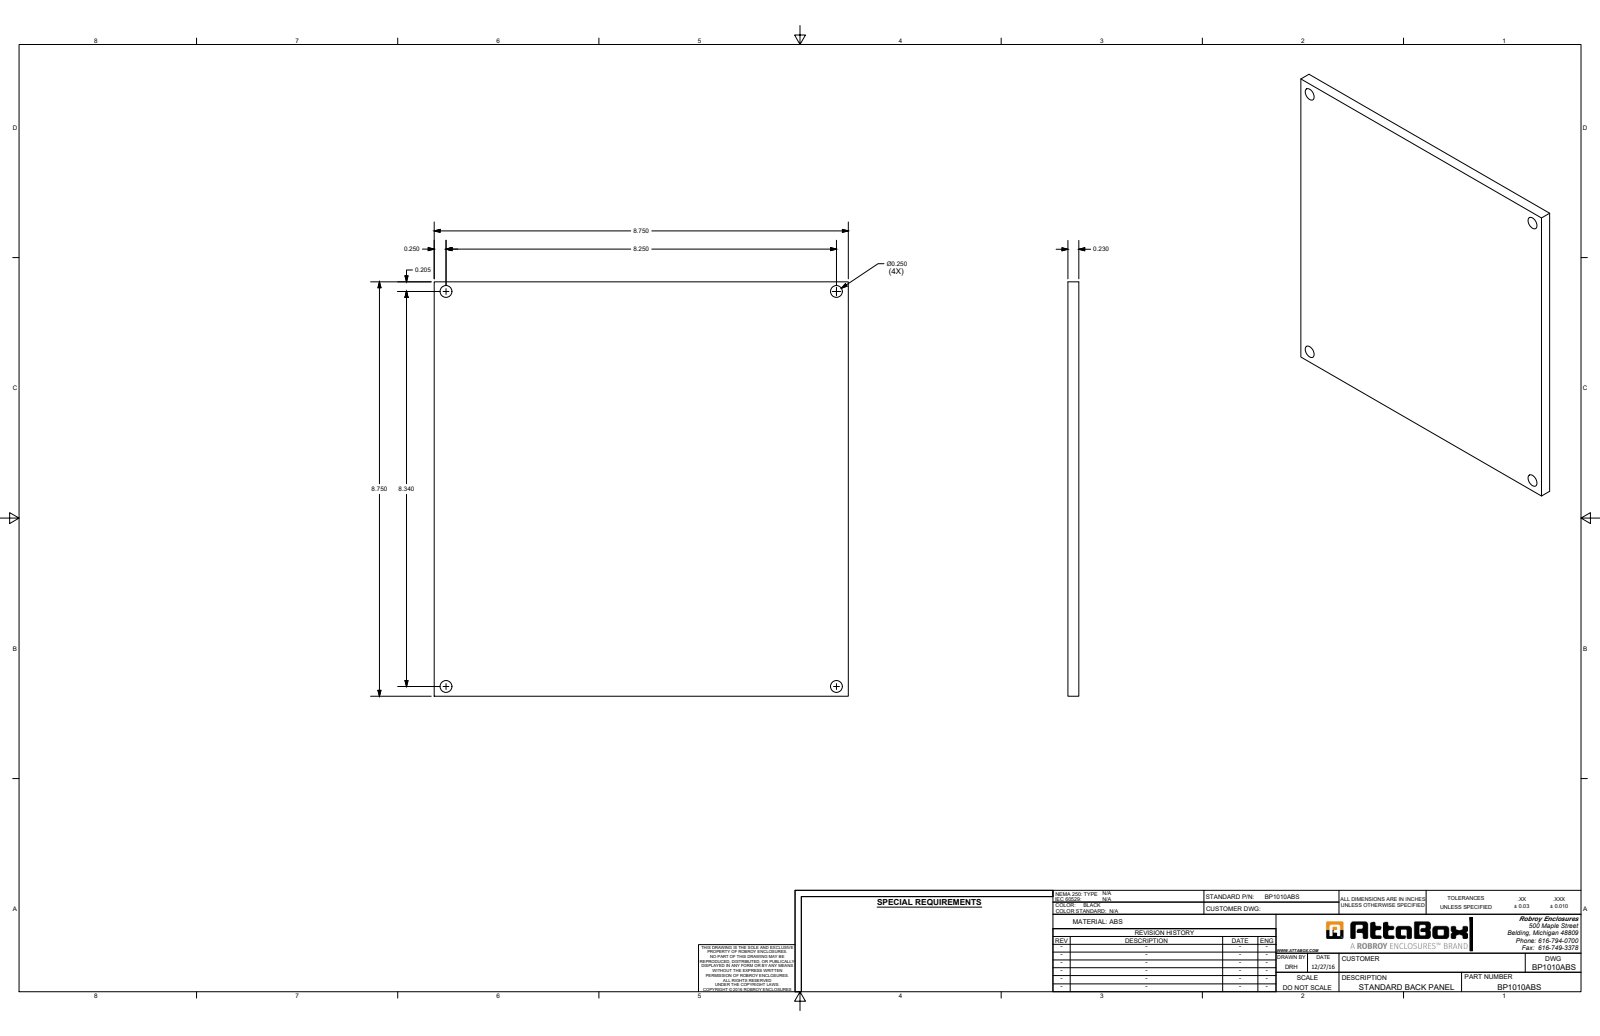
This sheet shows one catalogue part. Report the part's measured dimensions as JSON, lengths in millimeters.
{"part_name": "BP1010ABS_Default", "step_written_by": "SolidWorks 2023 (CONFIG_CONTROL_DESIGN)", "units": "millimeters", "bodies": {"solids": 1, "faces": 10, "planar": 6, "cylindrical": 4, "other": 0}, "overall_size": [222.3, 222.3, 5.8], "volume_mm3": 287800, "surface_area_mm2": 104200, "round_holes": [[6.4, 4]], "face_to_face_distances": [5.8, 222.3], "hole_center_spacings": [209.6, 296.3]}
